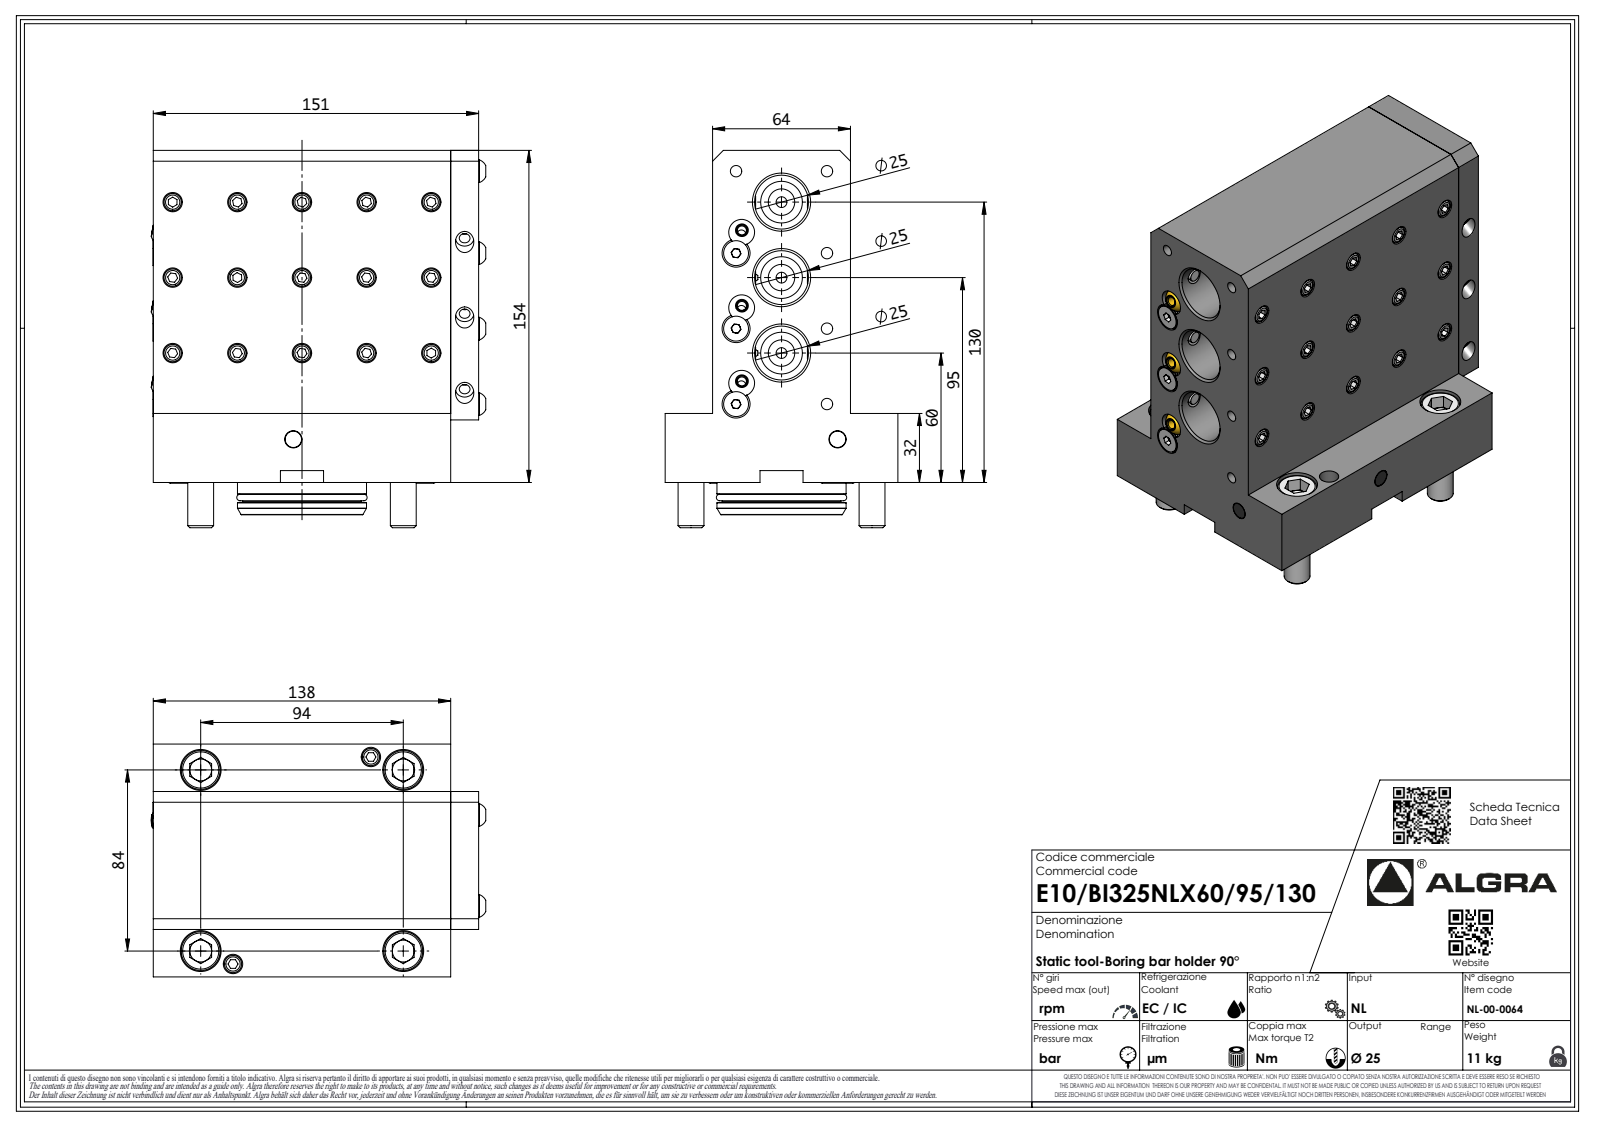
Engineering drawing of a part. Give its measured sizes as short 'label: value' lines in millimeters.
name: E10BI325NLX6095130
written by: SolidWorks 2023 (AUTOMOTIVE_DESIGN)
unit: mm
bodies: 1 solid, 422 faces (266 planar, 36 cylindrical, 120 other)
size: 175 × 151 × 108
volume: 1 687 000 mm³; area: 107 245 mm²
holes: 3× ⌀25, 1× ⌀2.1
bosses: 4× ⌀12, 1× ⌀59.9, 1× ⌀55, 1× ⌀6.37, 1× ⌀1.7
rounds: 7× R0.33, 7× R0.52, 7× R3.7, 1× R0.21
face distances: 64, 22, 86, 154, 151, 32, 122, 108, 13, 138
hole spacings: 35, 70
